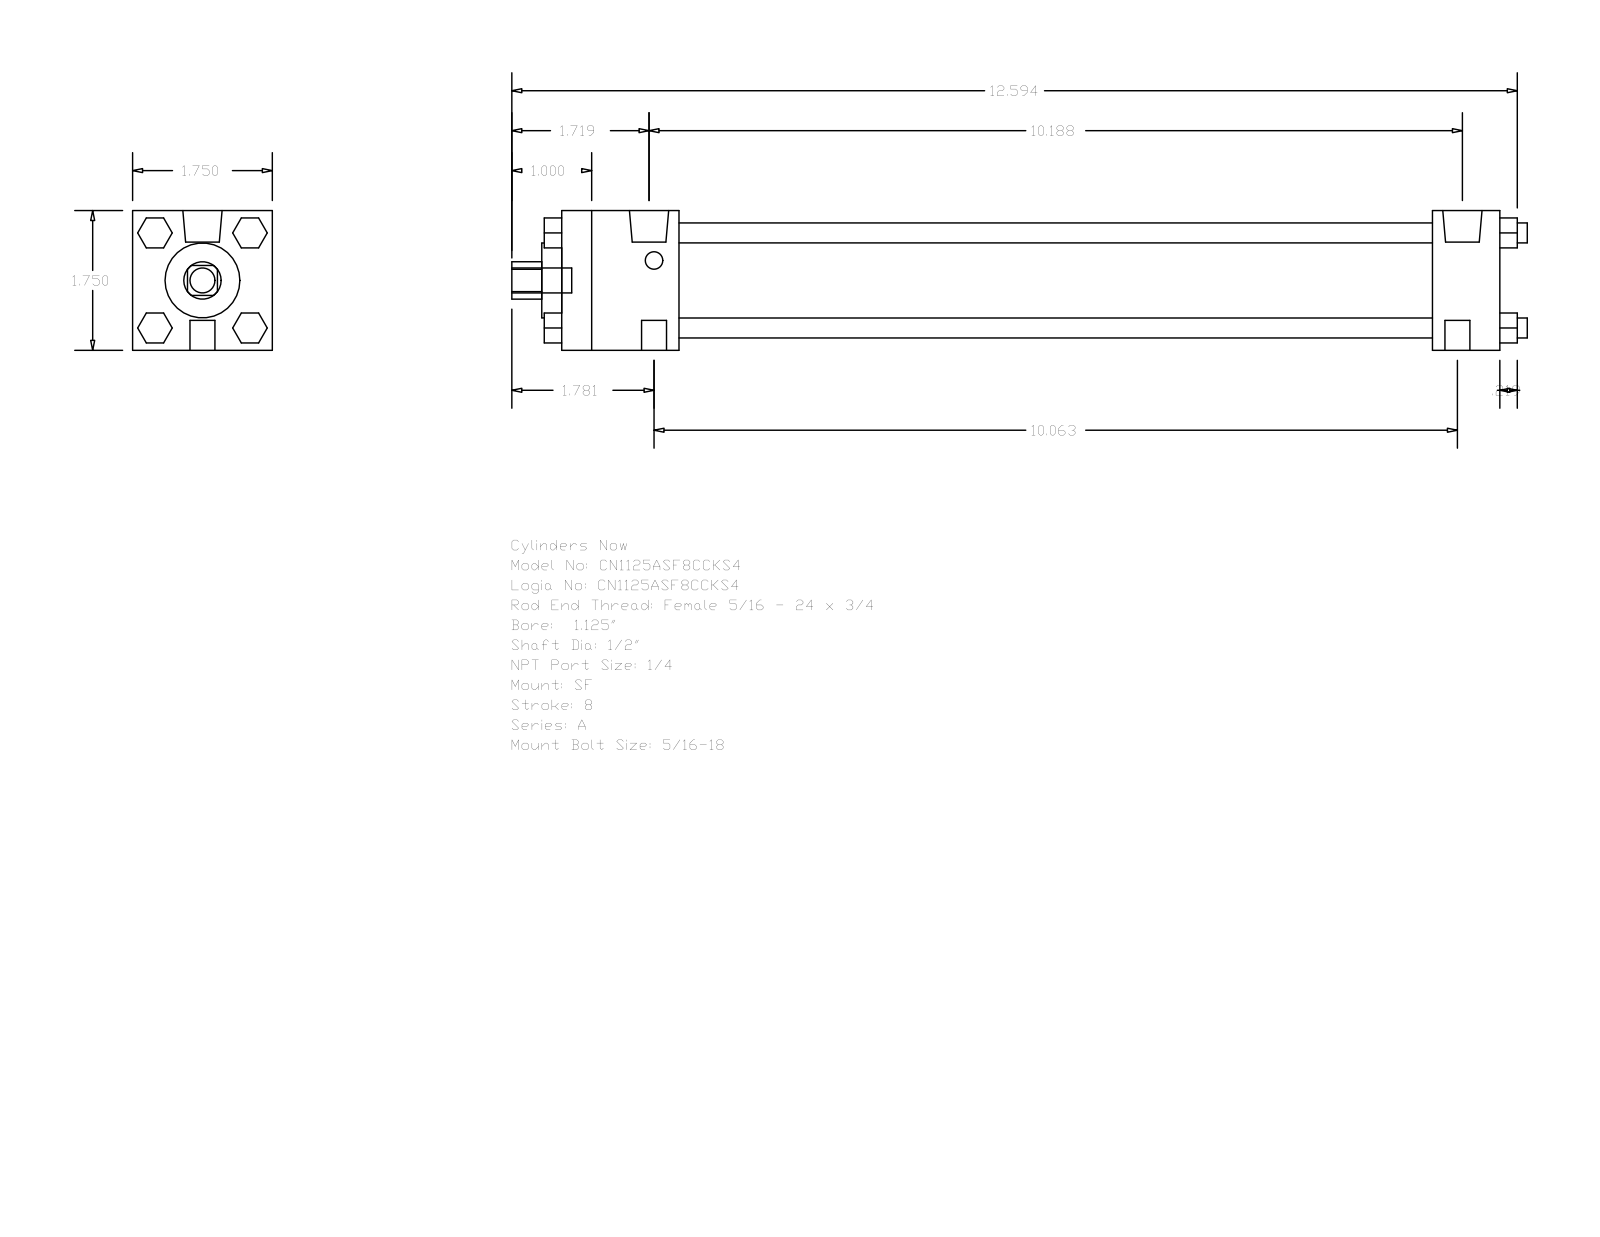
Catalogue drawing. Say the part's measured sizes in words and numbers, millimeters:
The part is named "A_SF__0112_0.5". Its 3-D file was written by "GSSL Pune (CONFIG_CONTROL_DESIGN)". It is 0 solids with 120 faces: 92 planar, 28 cylindrical and 0 other. Overall it measures 323.06 by 44.45 by 44.45 millimeters. Round holes: 1 of diameter 12.7, 1 of diameter 23.81, 1 of diameter 31.88. Round bosses or shafts: 4 of diameter 6.35, 3 of diameter 7.94, 2 of diameter 12.49, 2 of diameter 5.56. Partial cylindrical surfaces (rounded edges, fillets, slot ends): 1 of radius 5.94. The main face-to-face distances are 44.46, 298.44, 277.01, 21.43, 37.3, 239.71, 261.14, 9.53, 5.59, 9.52.
